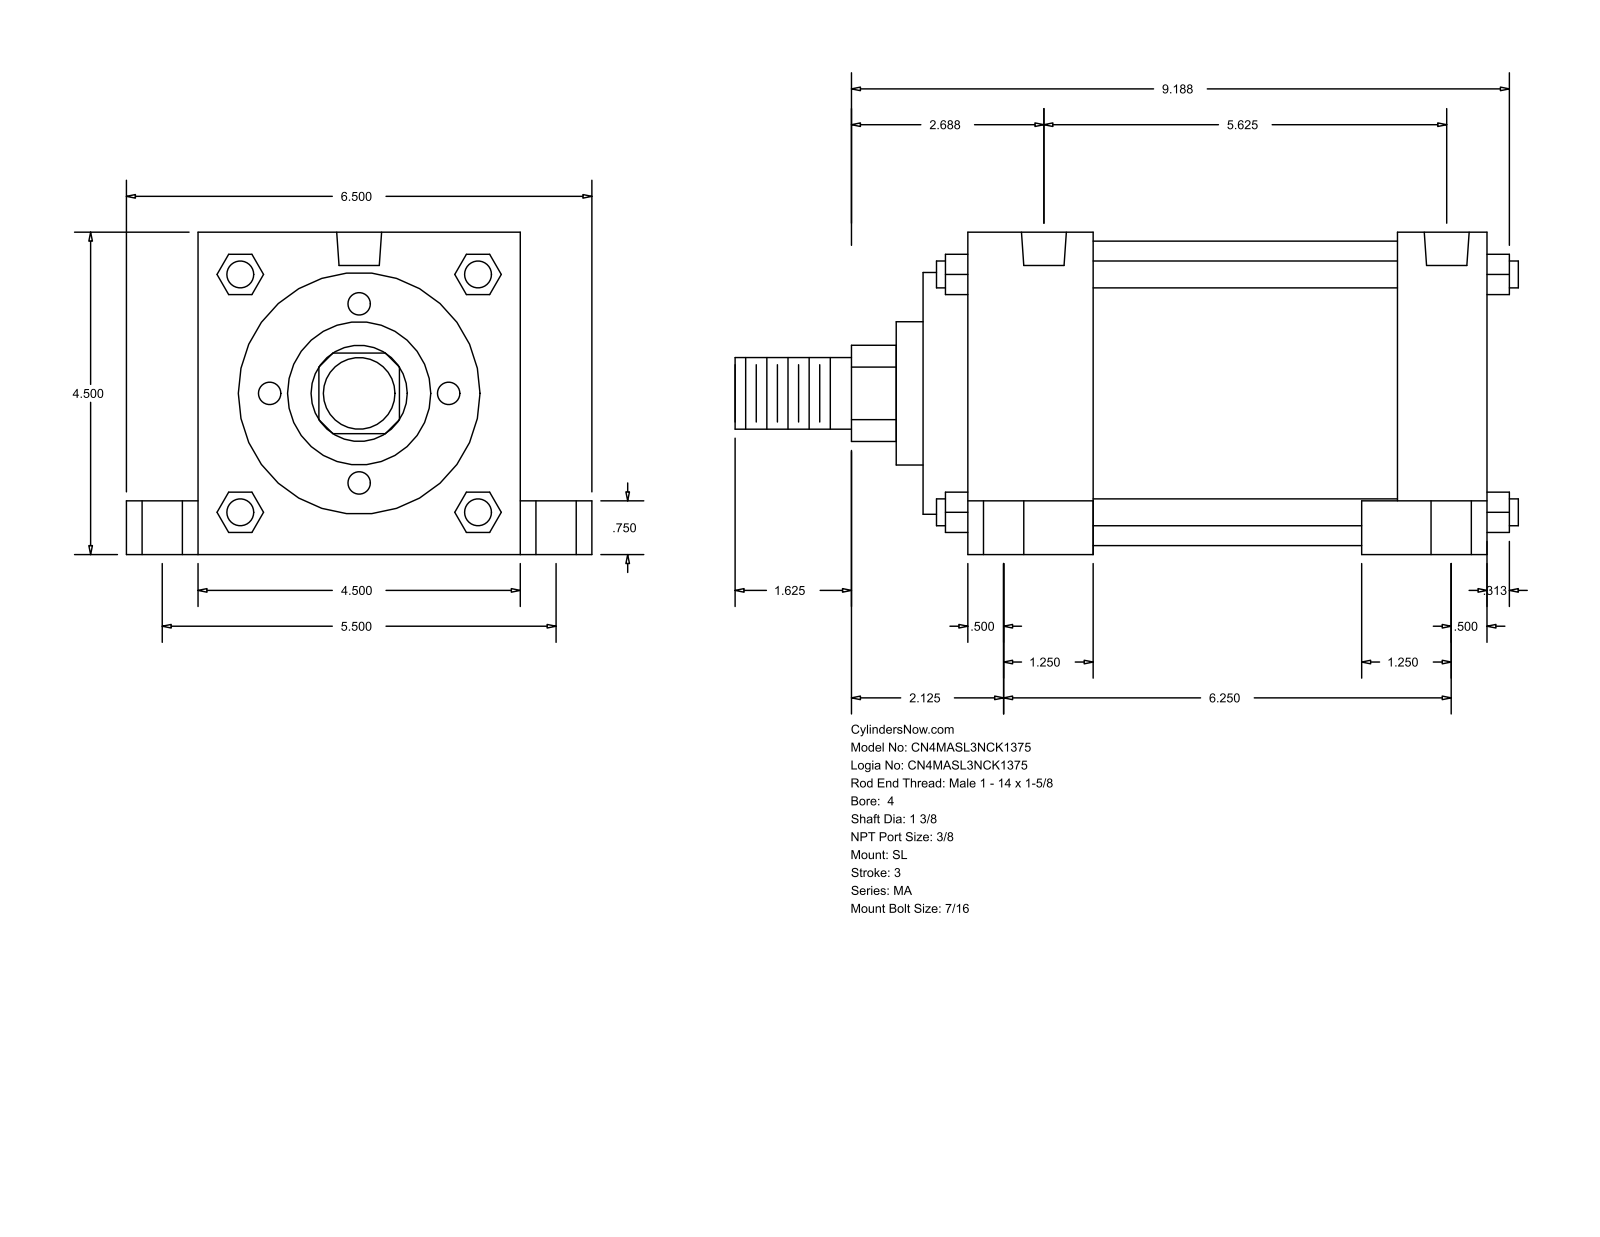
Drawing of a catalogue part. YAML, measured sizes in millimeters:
part_name: "MA_SL__0400_1.375"
step_written_by: "GSSL Pune (CONFIG_CONTROL_DESIGN)"
units: millimeters
bodies: {solids: 0, faces: 150, planar: 113, cylindrical: 37, other: 0}
overall_size: [277.81, 165.1, 114.3]
round_holes:
  - {diameter: 11.11, count: 4}
  - {diameter: 14.29, count: 4}
  - {diameter: 20.64, count: 4}
  - {diameter: 15.93, count: 2}
round_bosses_or_shafts:
  - {diameter: 9.53, count: 4}
  - {diameter: 107.95, count: 1}
  - {diameter: 85.72, count: 1}
  - {diameter: 50.8, count: 1}
  - {diameter: 34.92, count: 1}
  - {diameter: 25.4, count: 1}
partial_cylinders:
  - {radius: 17.06, count: 1}
face_to_face_distances: [114.3, 184.16, 15.87, 200.03, 60.32, 44.45, 139.71, 168.28, 152.41, 107.96]
hole_center_spacings: [69.87, 70.14, 71.29, 72.4, 133.35, 139.7, 156.18, 158.74]
